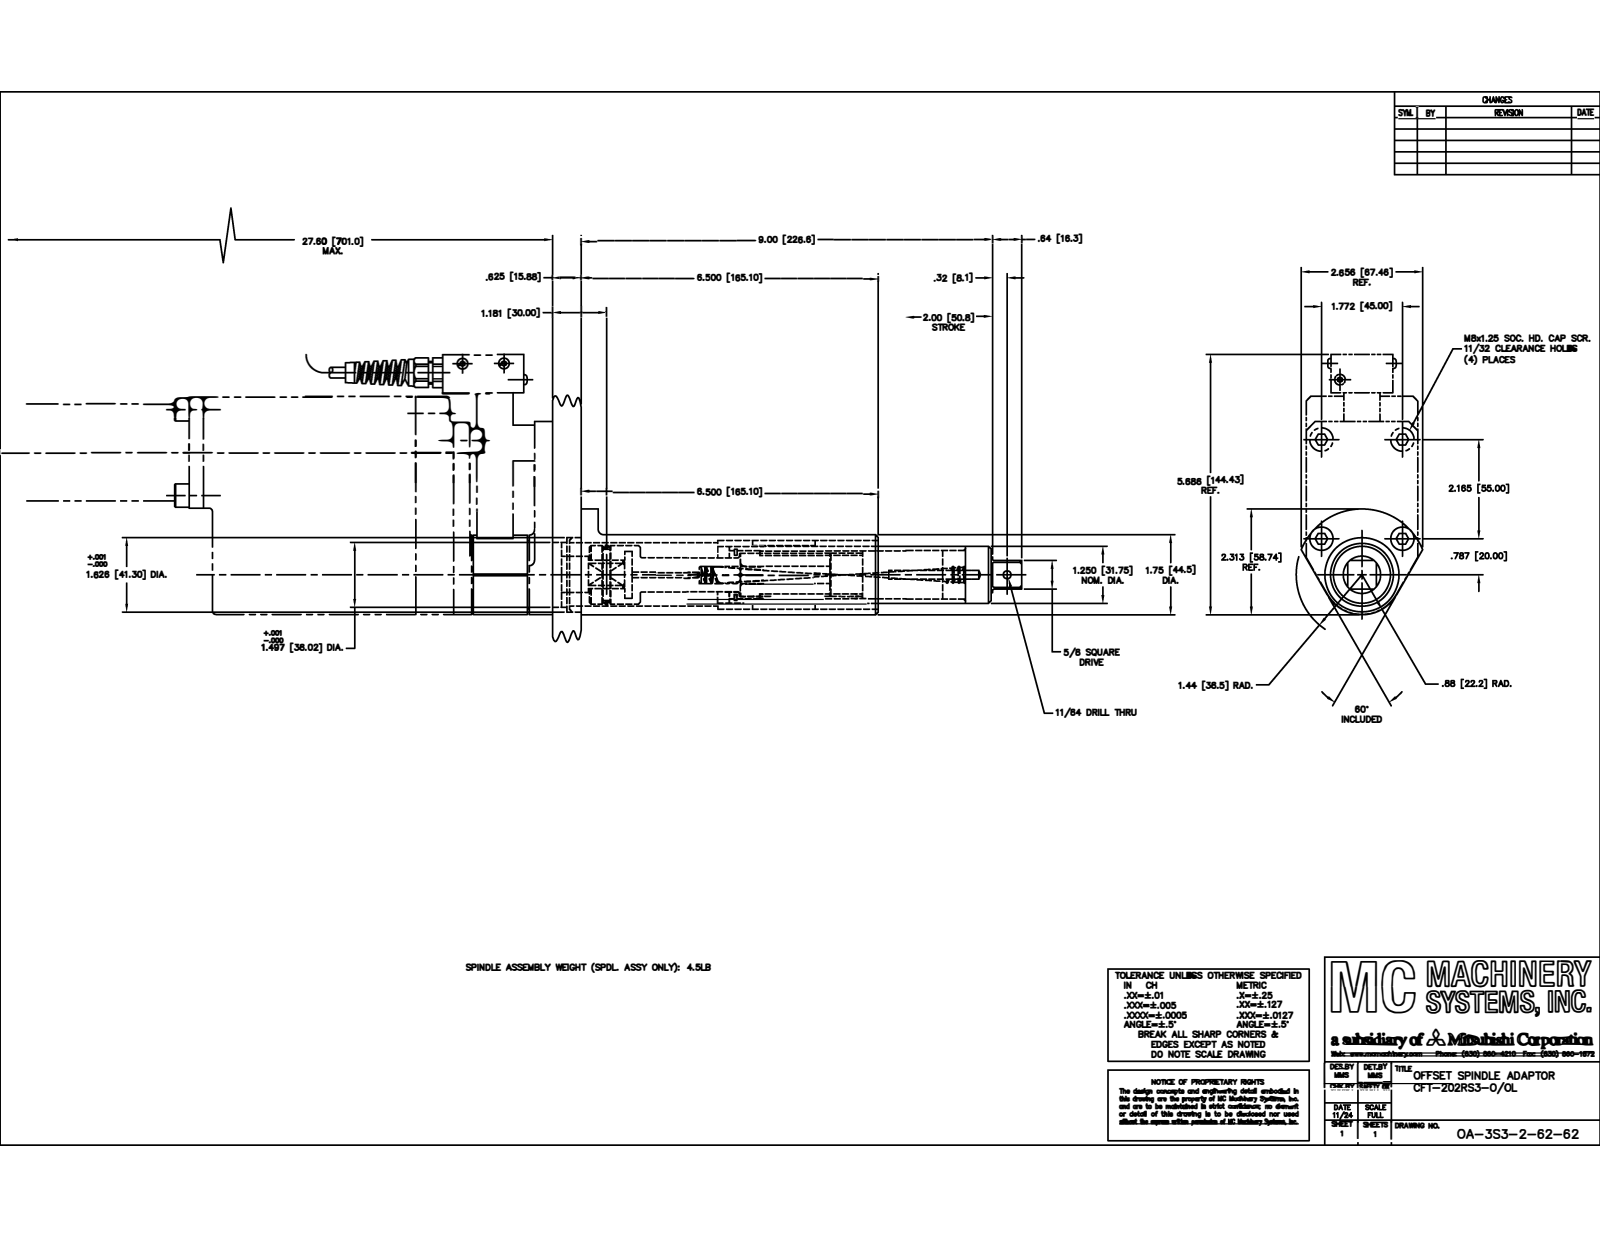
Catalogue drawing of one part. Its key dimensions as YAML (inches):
part_name: "SA-158H; R-6-12-6.50-20-1; OA-3S3-62-62"
step_written_by: "SolidWorks 2013 (CONFIG_CONTROL_DESIGN)"
units: inches
bodies: {solids: 2, faces: 49, planar: 19, cylindrical: 21, other: 9}
overall_size: [9.89, 2.36, 2.312]
volume: 17.07
surface_area: 101.2
round_holes:
  - {diameter: 0.344, count: 2}
  - {diameter: 0.203, count: 1}
  - {diameter: 1.25, count: 1}
round_bosses_or_shafts:
  - {diameter: 1.75, count: 1}
  - {diameter: 1.625, count: 1}
  - {diameter: 0.834, count: 1}
partial_cylinders:
  - {radius: 0.047, count: 4}
  - {radius: 1.437, count: 1}
face_to_face_distances: [0.375, 2.14, 1.765, 0.625, 6.5, 6.125, 4.36, 8.97, 8.595, 6.83]
hole_center_spacings: [1.185, 1.772]
